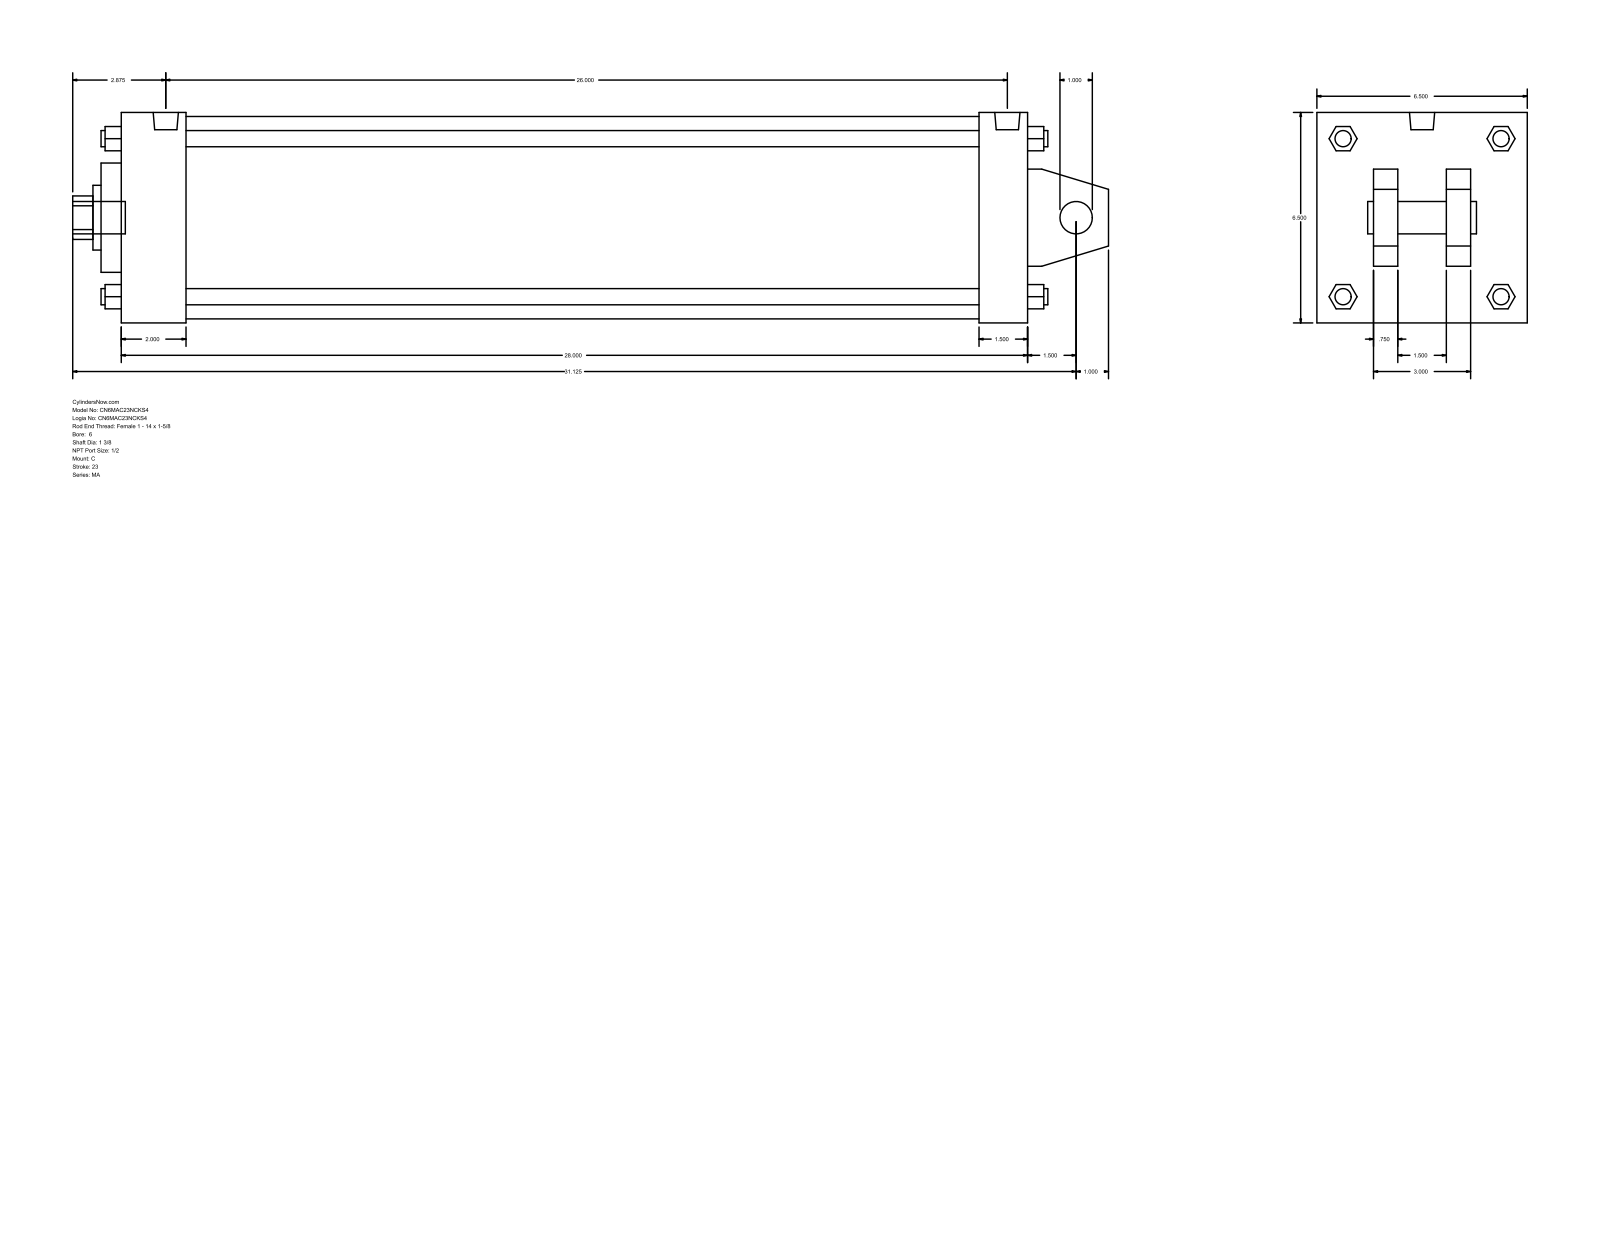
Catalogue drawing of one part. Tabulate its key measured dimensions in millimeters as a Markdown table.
| quantity | value |
| --- | --- |
| part name | MA_C__0600_1.375 |
| STEP written by | GSSL Pune (CONFIG_CONTROL_DESIGN) |
| units | millimeters |
| bodies | 0 solids, 141 faces (109 planar, 32 cylindrical, 0 other) |
| overall size | 812.8 × 165.1 × 165.1 |
| round holes (diameter × count) | 25.4 × 1, 34.92 × 1, 50.8 × 1, 85.72 × 1, 158.75 × 1 |
| round bosses / shafts (diameter × count) | 17.46 × 4, 12.7 × 4, 19.77 × 2, 25.4 × 1 |
| partial cylindrical surfaces (radius × count) | 17.06 × 1 |
| main face-to-face distances | 165.1, 711.2, 38.1, 19.05, 63.5, 101.6, 50.8, 44.45, 120.65, 673.1 |
